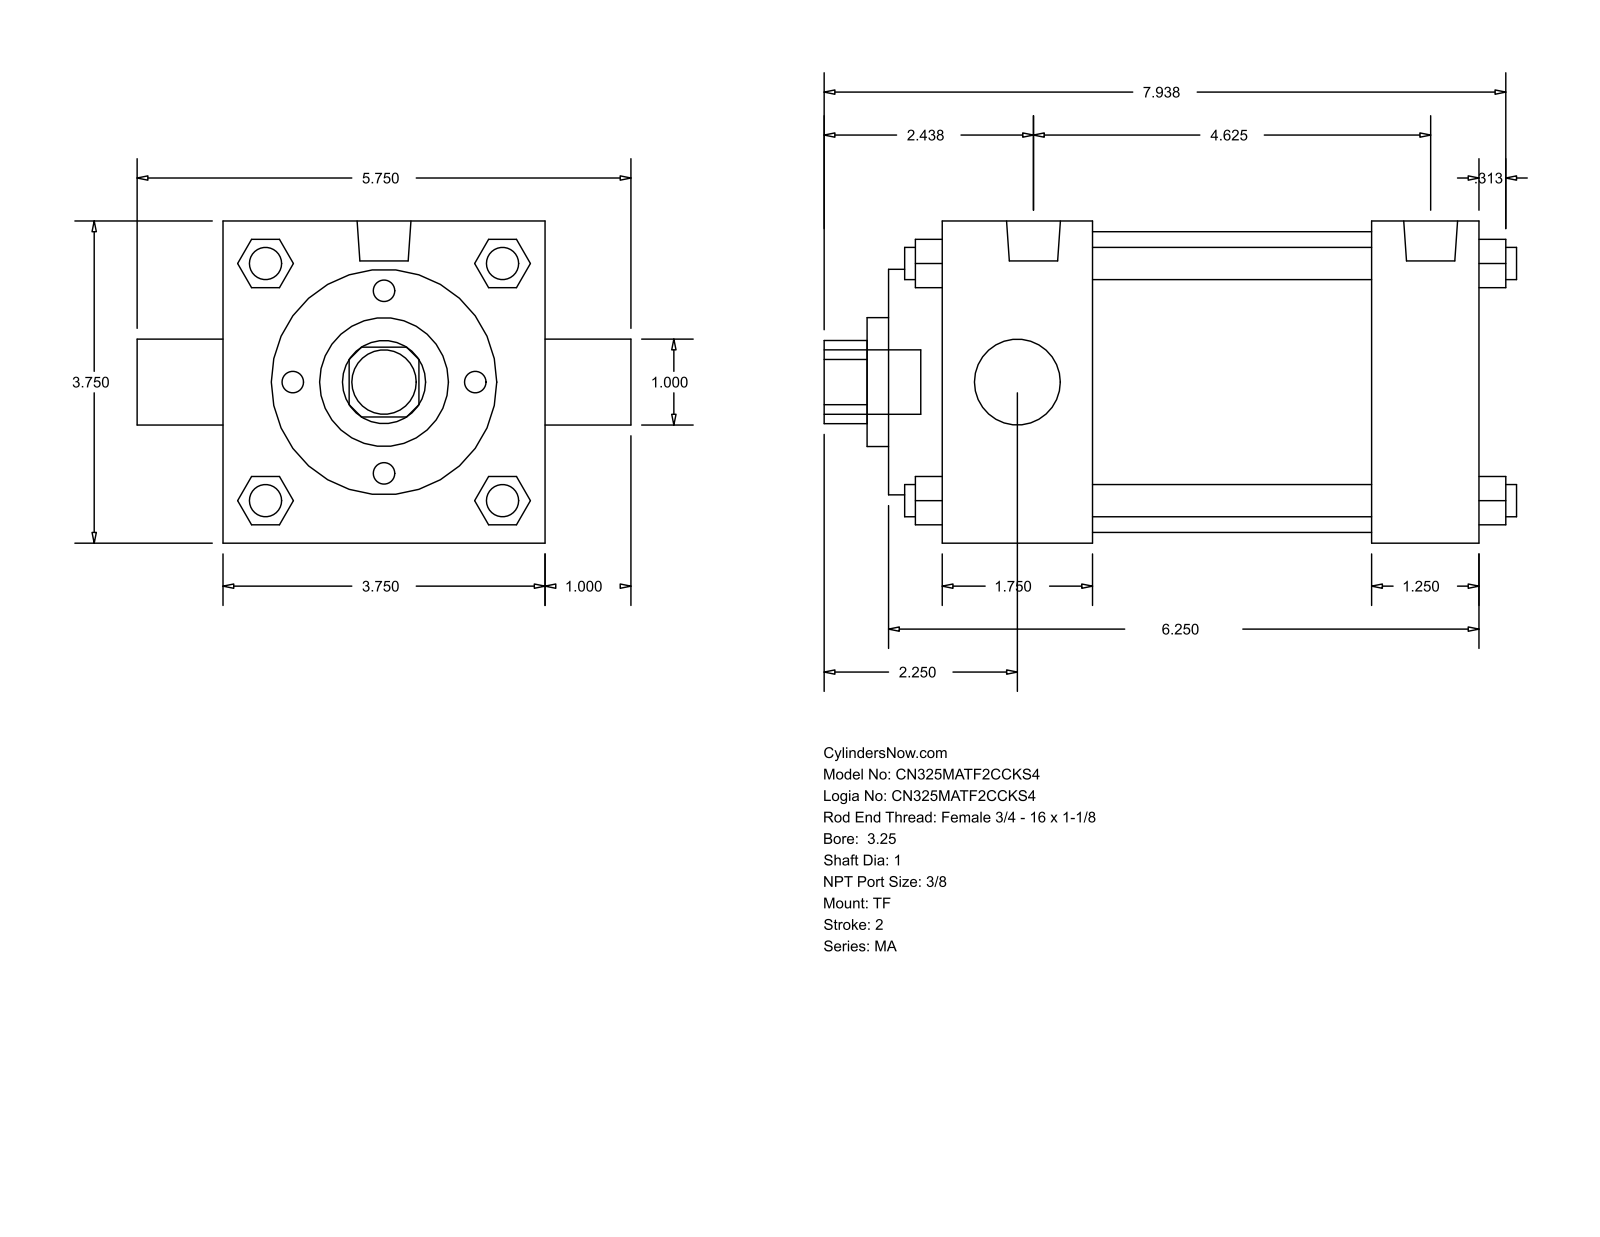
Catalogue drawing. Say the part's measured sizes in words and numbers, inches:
The part is named "MA_TF__0325_1". Its 3-D file was written by "GSSL Pune (CONFIG_CONTROL_DESIGN)". It is 0 solids with 122 faces: 93 planar, 29 cylindrical and 0 other. Overall it measures 8.063 by 5.75 by 3.75 inches. Round holes: 2 of diameter 1, 1 of diameter 1.5, 1 of diameter 2.625, 1 of diameter 3.5. Round bosses or shafts: 4 of diameter 0.375, 3 of diameter 0.437, 2 of diameter 0.627, 1 of diameter 0.75. Partial cylindrical surfaces (rounded edges, fillets, slot ends): 1 of radius 0.484. The main face-to-face distances are 3.75, 6.25, 0.625, 1.75, 5, 3.25, 4.5, 1.25, 2.375, 5.625.
